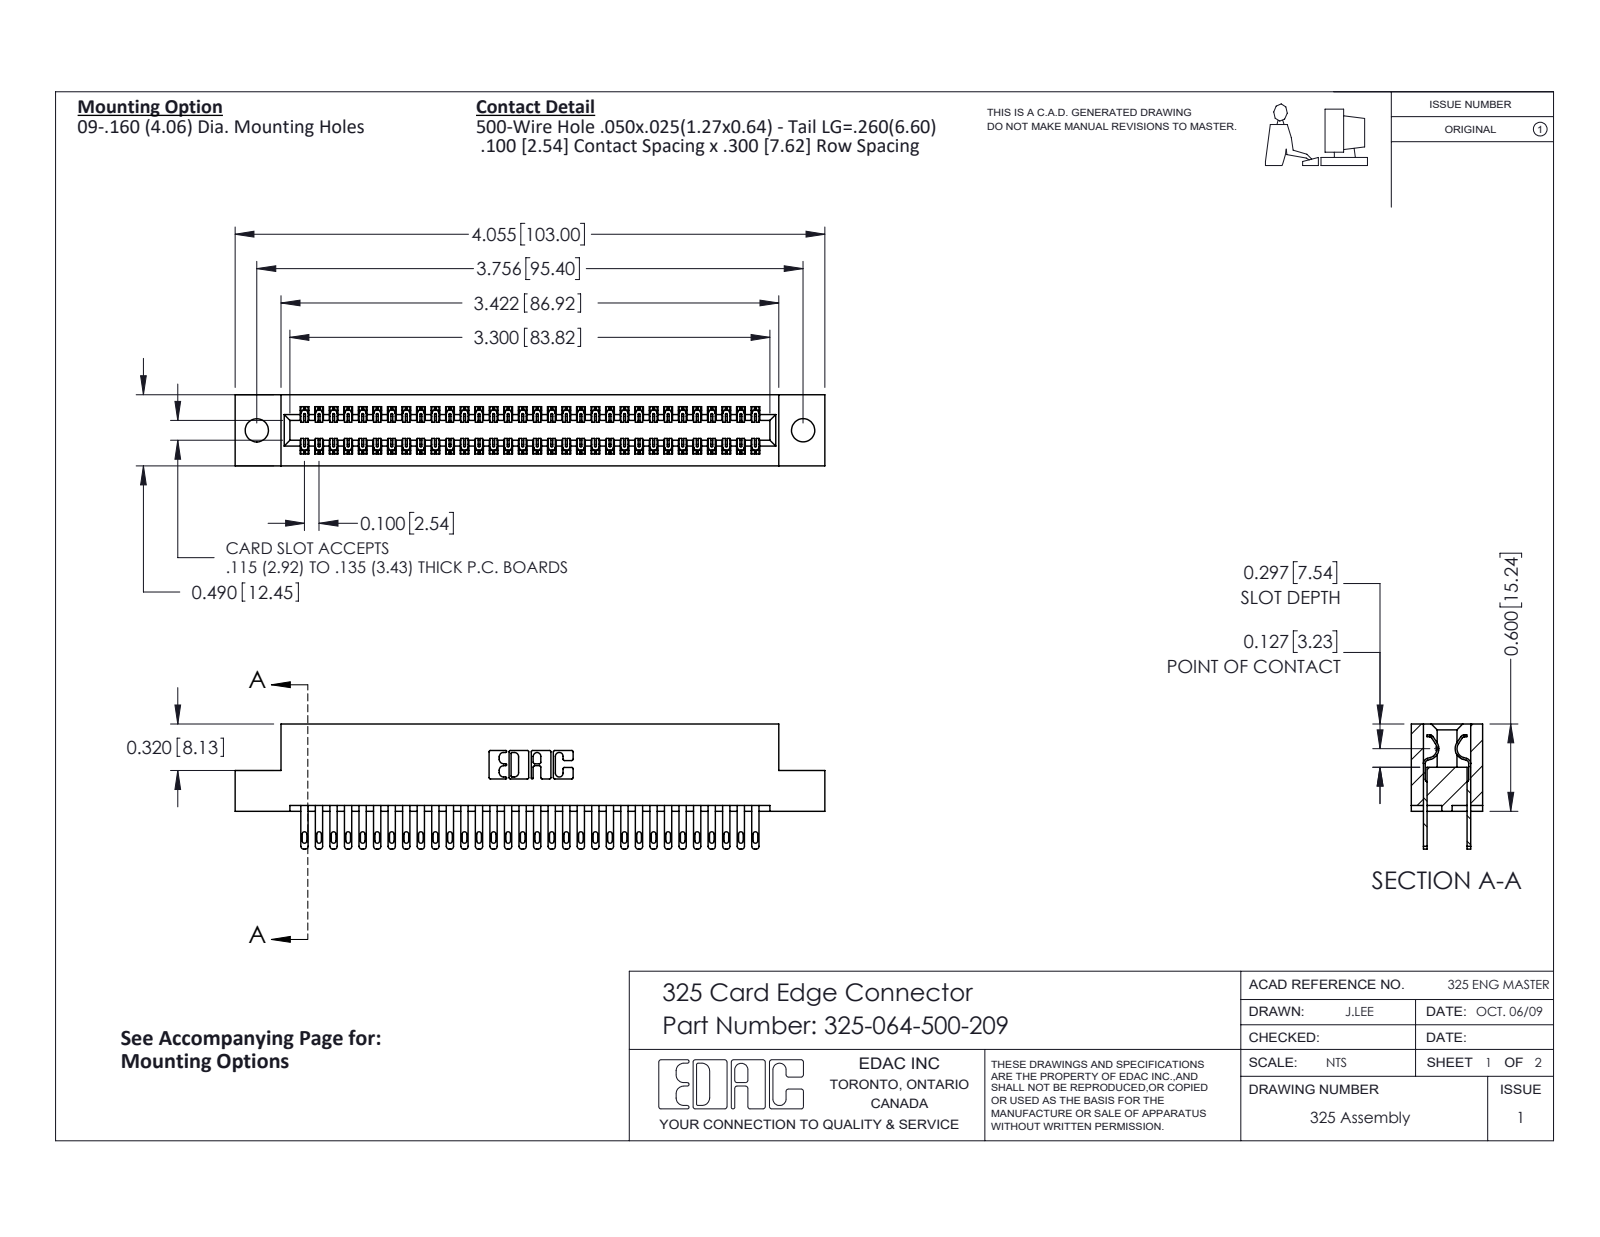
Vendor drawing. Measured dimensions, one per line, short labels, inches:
name: 325-064-500-209; 325-292-001_325-293-100; 325 Part_.160 TH
written by: SolidWorks 2016 (CONFIG_CONTROL_DESIGN)
unit: in
bodies: 65 solids, 3186 faces (1990 planar, 1196 cylindrical, 0 other)
size: 4.055 × 0.86 × 0.49
volume: 0.804 in³; area: 25.26 in²
holes: 2× ⌀0.16
rounds: 96× R0.006, 64× R0.016, 64× R0.02, 22× R0.01, 6× R0.007, 6× R0.031, 3× R0.026, 2× R0.014
face distances: 0.083, 0.407, 0.3, 0.107, 0.383, 0.025, 0.49, 0.325, 0.275, 0.04
hole spacings: 3.756
